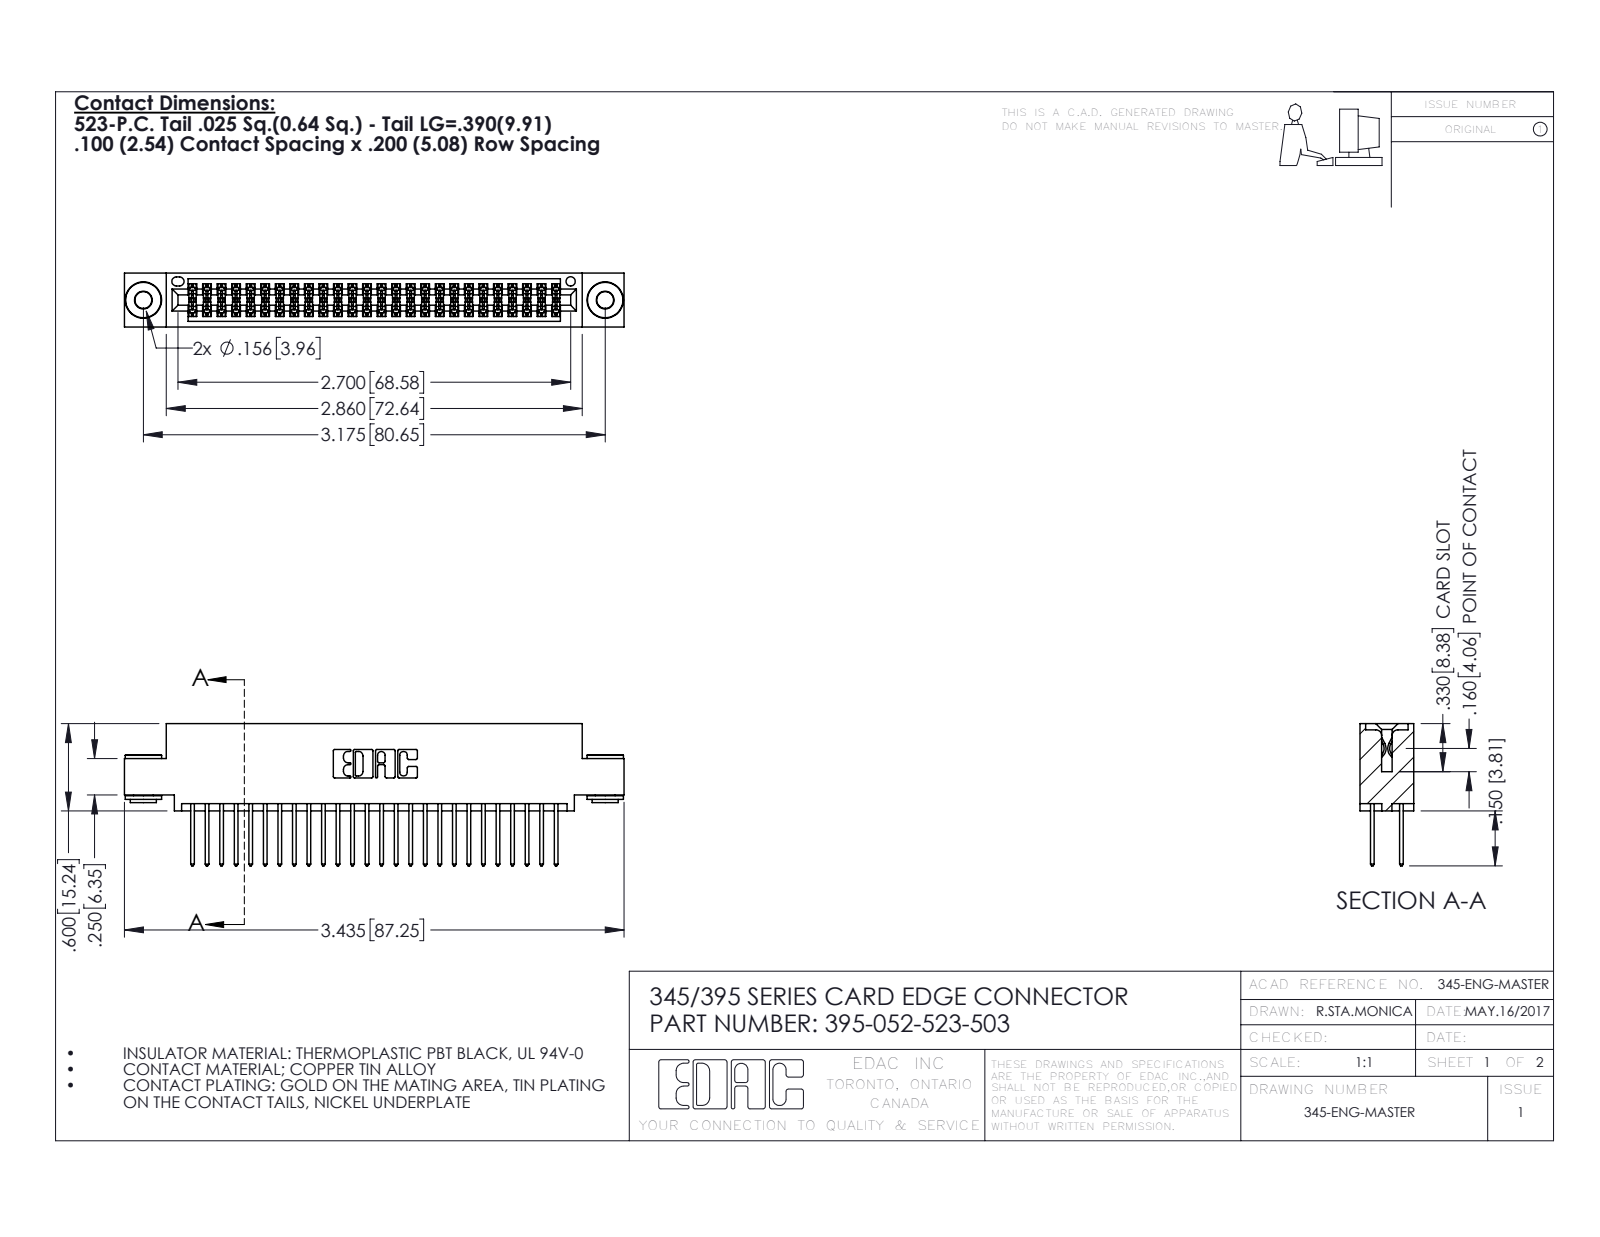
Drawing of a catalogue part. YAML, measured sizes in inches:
part_name: "345-292-001_345-293-123; 345 Part_0.110 Offset - 0.156 Dia-TH; 345-250-002_345-250-002-102; 395-052-523-503"
step_written_by: "SolidWorks 2016 (CONFIG_CONTROL_DESIGN)"
units: inches
bodies: {solids: 55, faces: 2768, planar: 1810, cylindrical: 950, other: 8}
overall_size: [3.435, 0.977, 0.37]
volume: 0.511
surface_area: 19.92
round_holes:
  - {diameter: 0.116, count: 2}
  - {diameter: 0.156, count: 2}
  - {diameter: 0.064, count: 1}
round_bosses_or_shafts:
  - {diameter: 0.25, count: 2}
  - {diameter: 0.18, count: 2}
  - {diameter: 0.136, count: 2}
partial_cylinders:
  - {radius: 0.006, count: 78}
  - {radius: 0.01, count: 52}
  - {radius: 0.01, count: 22}
  - {radius: 0.007, count: 6}
  - {radius: 0.031, count: 6}
  - {radius: 0.026, count: 3}
  - {radius: 0.014, count: 2}
  - {radius: 0.019, count: 2}
face_to_face_distances: [0.072, 0.298, 0.2, 0.025, 0.098, 0.272, 0.37, 0.225, 0.175, 0.149]
hole_center_spacings: [0.27, 2.94, 3.175]
